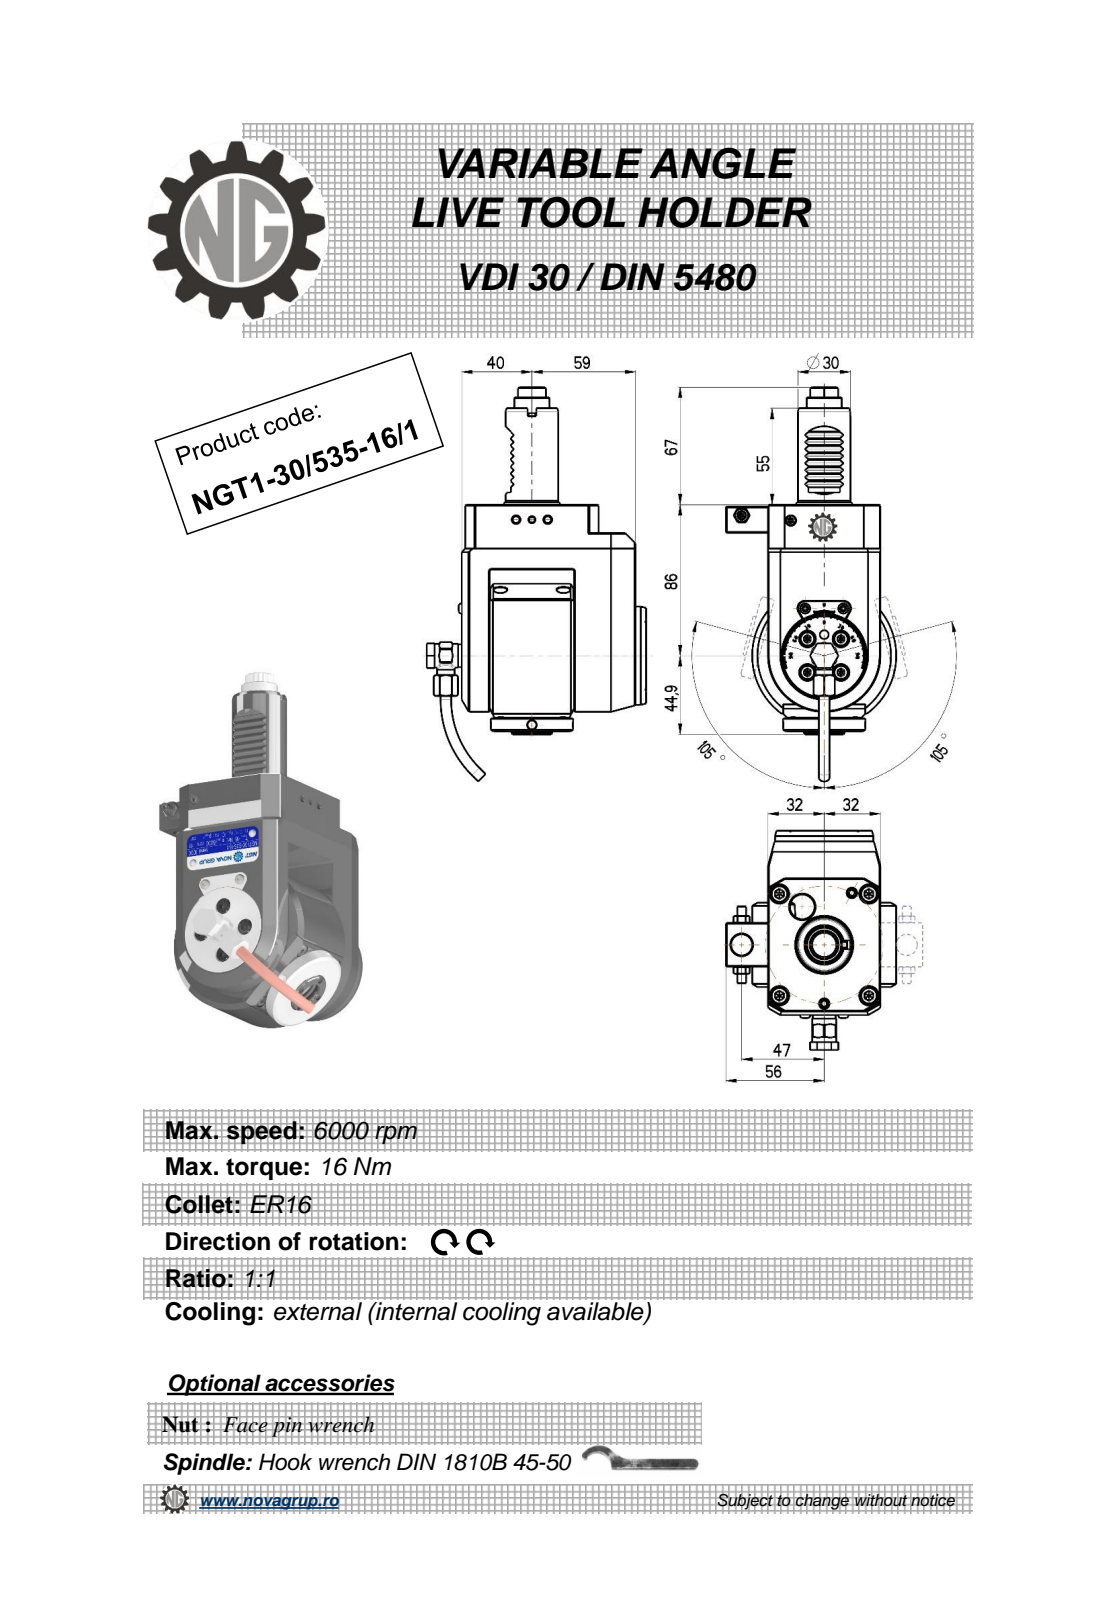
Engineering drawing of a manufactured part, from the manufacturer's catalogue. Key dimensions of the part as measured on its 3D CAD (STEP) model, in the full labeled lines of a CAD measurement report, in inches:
Part name (STEP PRODUCT): NGT1_30_535_16_1
STEP written by: PRO/ENGINEER BY PARAMETRIC TECHNOLOGY CORPORATION, 2010280 (CONFIG_CONTROL_DESIGN)
Units: inches
Bodies: 1 solid, 580 faces (206 planar, 207 cylindrical, 167 other)
Overall size (bounding box): 8.845 × 4.917 × 3.819
Volume: 46.63 in³ · Surface area: 112.5 in²
Round holes (diameter × count): ⌀0.126 ×4, ⌀0.157 ×3, ⌀0.197 ×2, ⌀0.118 ×1, ⌀0.165 ×1, ⌀0.244 ×1, ⌀0.354 ×1, ⌀0.374 ×1, ⌀0.433 ×1, ⌀0.472 ×1, ⌀0.492 ×1
Round bosses / shafts (diameter × count): ⌀0.394 ×2, ⌀0.236 ×2, ⌀0.224 ×2, ⌀3.228 ×1, ⌀2.205 ×1, ⌀1.85 ×1, ⌀1.378 ×1, ⌀1.181 ×1
Partial cylindrical surfaces — rounded edges, fillets, slot ends (radius × count): R0.078 ×36, R0.01 ×12, R0.012 ×8, R0.006 ×6, R0.02 ×4, R0.039 ×2, R0.287 ×1, R0.303 ×1
Main face-to-face distances: 2.52, 0.63, 1.457, 3.898, 0.236, 4.134, 0.827, 3.268, 0.551, 1.378
Hole centre spacings: 0.364, 0.515, 0.728, 1.886, 1.963, 1.979, 0.016, 1.486
